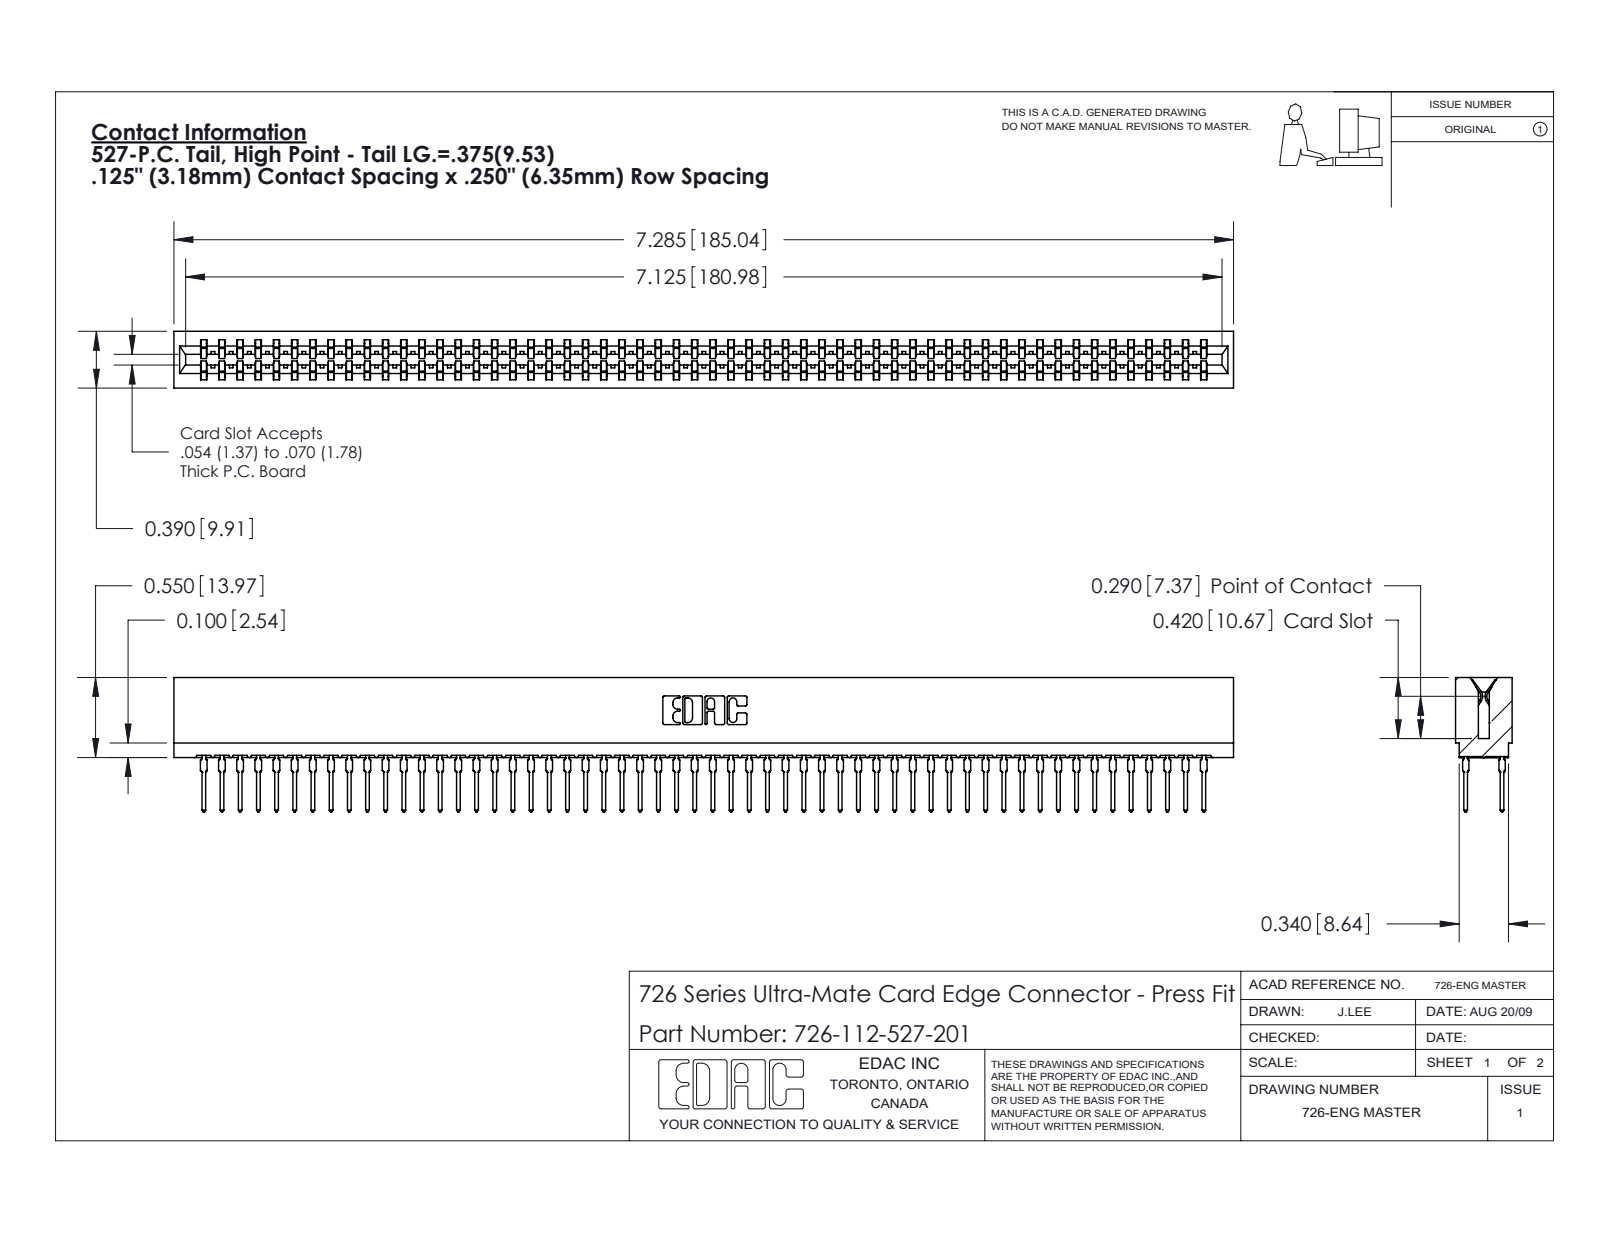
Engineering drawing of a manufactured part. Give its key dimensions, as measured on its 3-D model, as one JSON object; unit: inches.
{"part_name": "746-292-001_527; 726-112-527-201; 726 Part_.515 Slot Depth - 01", "step_written_by": "SolidWorks 2020 (CONFIG_CONTROL_DESIGN)", "units": "inches", "bodies": {"solids": 113, "faces": 10121, "planar": 5207, "cylindrical": 2002, "other": 2912}, "overall_size": [7.285, 0.924, 0.39], "volume_in3": 1.046, "surface_area_in2": 46.03, "partial_cylinders_radius": [[0.021, 224], [0.015, 57], [0.01, 22], [0.005, 8], [0.011, 8], [0.007, 6], [0.031, 6], [0.026, 3]], "face_to_face_distances": [0.057, 0.333, 0.025, 0.307, 0.39, 0.25, 0.275, 0.083, 0.365, 0.032]}
